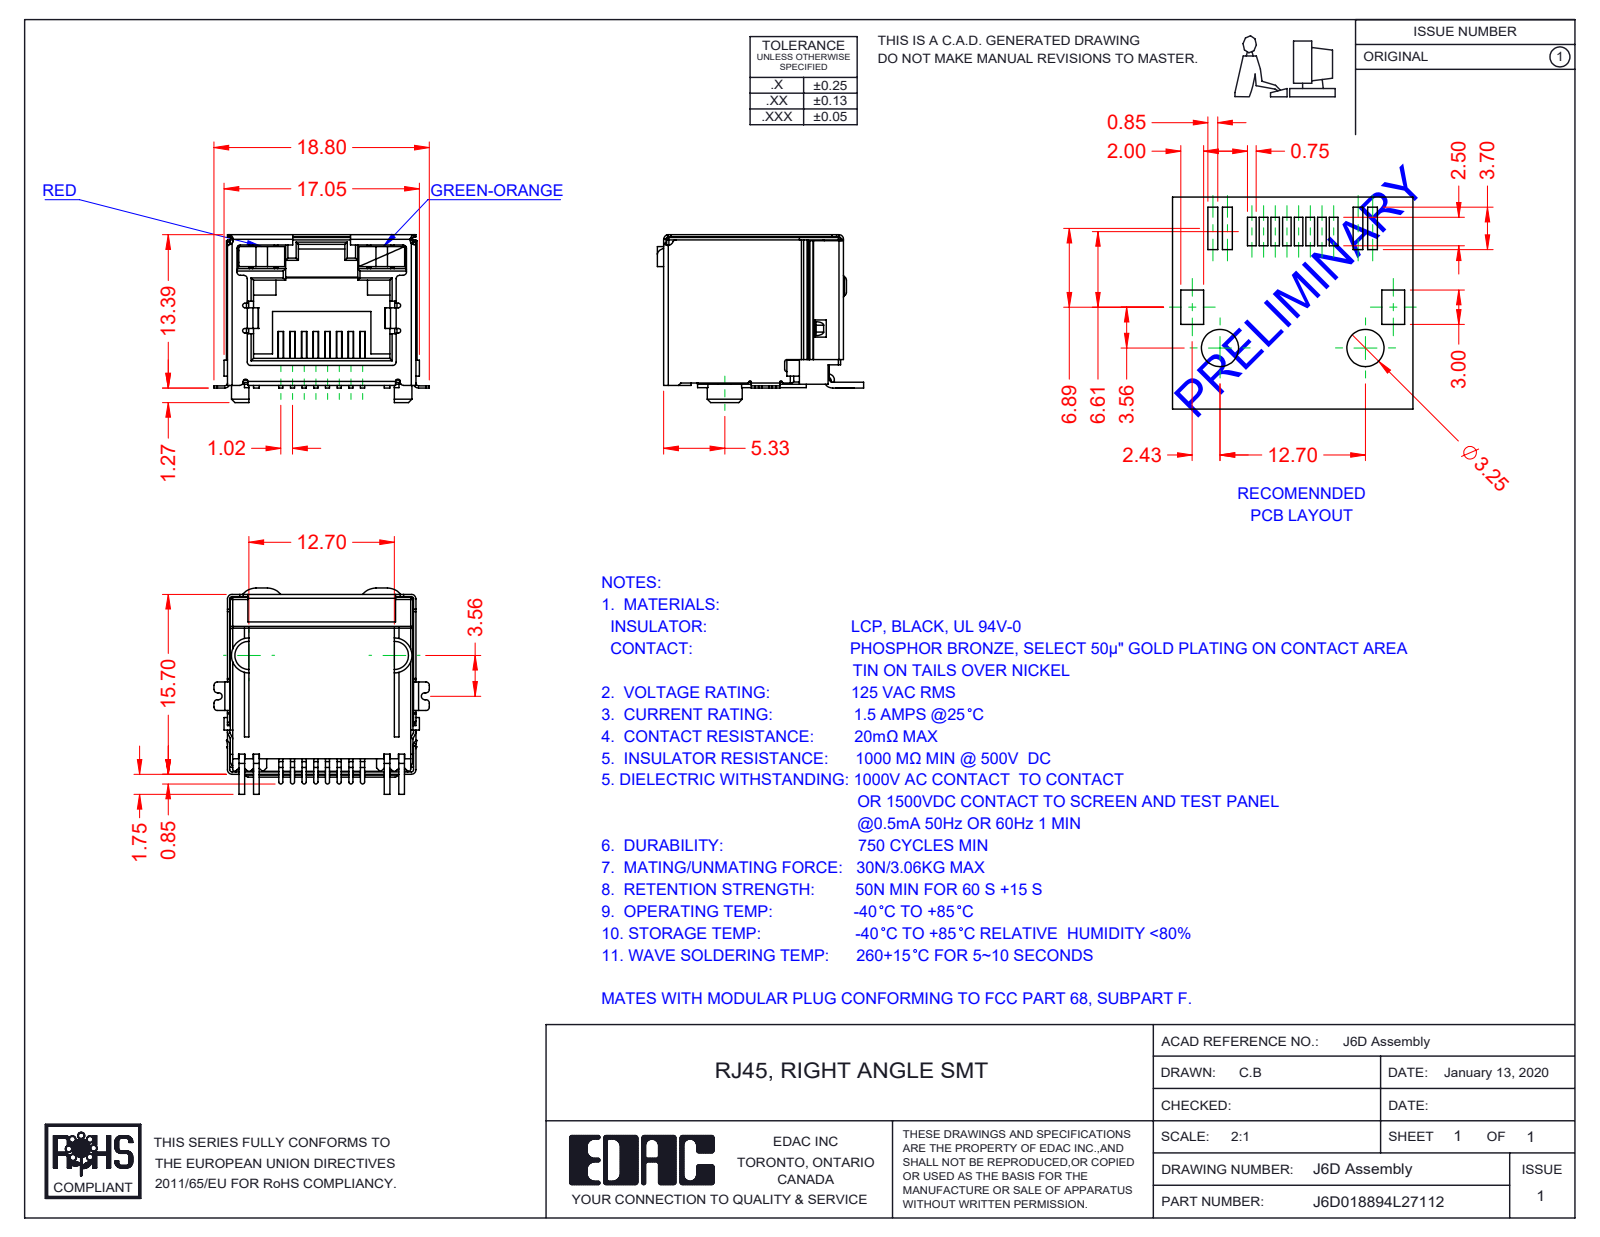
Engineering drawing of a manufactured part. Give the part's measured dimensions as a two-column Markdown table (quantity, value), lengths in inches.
| quantity | value |
| --- | --- |
| part name | 6D LED RH_7-Green-Orange; 6D Shield_LED - No EMI; 6D Contacts; 6D LED LH_2-Red (+2 more) |
| STEP written by | SolidWorks 2016 (CONFIG_CONTROL_DESIGN) |
| units | inches |
| bodies | 12 solids, 896 faces (645 planar, 218 cylindrical, 33 other) |
| overall size | 0.74 × 0.709 × 0.577 |
| volume | 0.11 in³ |
| surface area | 7.592 in² |
| partial cylindrical surfaces (radius × count) | 0.012 × 39, 0.008 × 37, 0.016 × 16, 0.004 × 12, 0.006 × 8, 0.007 × 8, 0.02 × 6, 0.059 × 5 |
| main face-to-face distances | 0.63, 0.64, 0.638, 0.089, 0.039, 0.628, 0.632, 0.504, 0.018, 0.648 |
